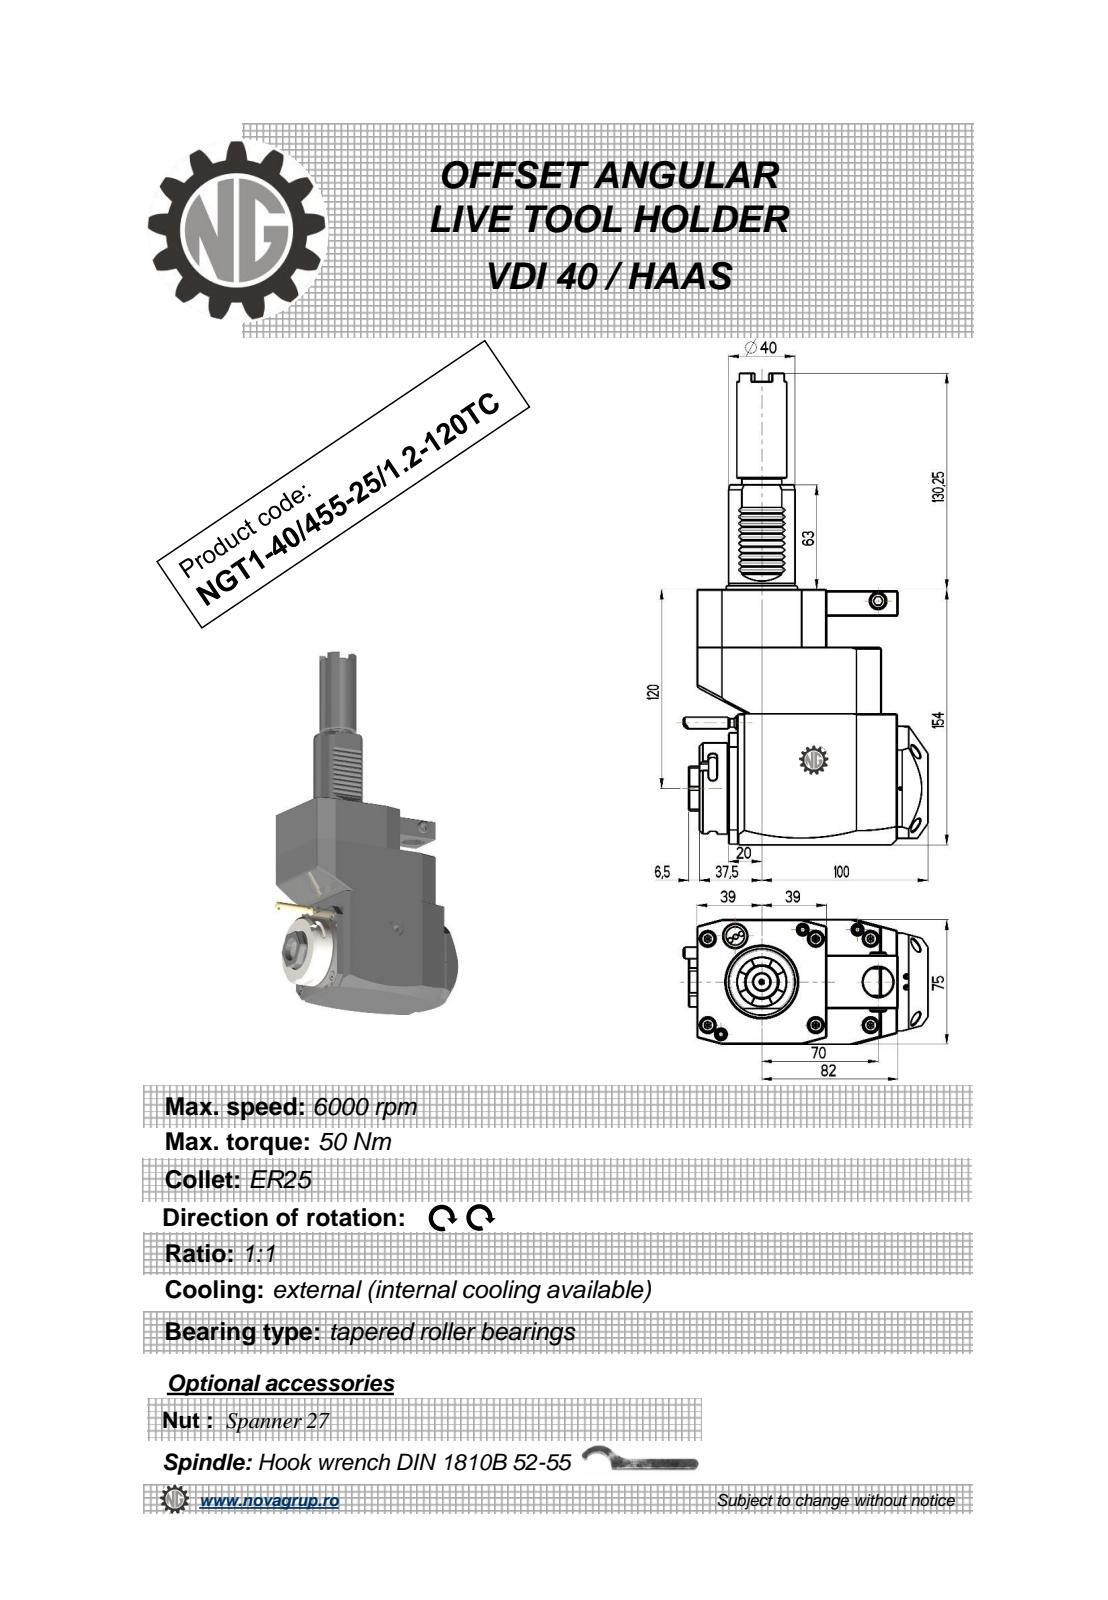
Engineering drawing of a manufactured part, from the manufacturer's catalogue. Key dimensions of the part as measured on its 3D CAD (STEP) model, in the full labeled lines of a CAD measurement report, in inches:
Part name (STEP PRODUCT): NGT1_40_455_25_1_2_120TC
STEP written by: PRO/ENGINEER BY PARAMETRIC TECHNOLOGY CORPORATION, 2010280 (CONFIG_CONTROL_DESIGN)
Units: inches
Bodies: 1 solid, 370 faces (216 planar, 70 cylindrical, 84 other)
Overall size (bounding box): 11.191 × 5.8 × 2.953
Volume: 80.19 in³ · Surface area: 150.8 in²
Round holes (diameter × count): ⌀0.709 ×2, ⌀0.098 ×1, ⌀0.118 ×1, ⌀0.374 ×1, ⌀0.787 ×1
Round bosses / shafts (diameter × count): ⌀0.353 ×2, ⌀2.165 ×1, ⌀1.89 ×1, ⌀1.575 ×1, ⌀1.181 ×1, ⌀0.945 ×1, ⌀0.394 ×1, ⌀0.276 ×1
Partial cylindrical surfaces — rounded edges, fillets, slot ends (radius × count): R0.012 ×10, R0.098 ×6, R7.087 ×2, R0.02 ×1, R0.167 ×1, R0.591 ×1, R0.965 ×1, R1.476 ×1
Main face-to-face distances: 2.953, 6.063, 0.748, 4.685, 2.323, 4.37, 3.622, 1.378, 0.689, 2.106
Hole centre spacings: 1.701, 2.756, 2.956, 4.429
